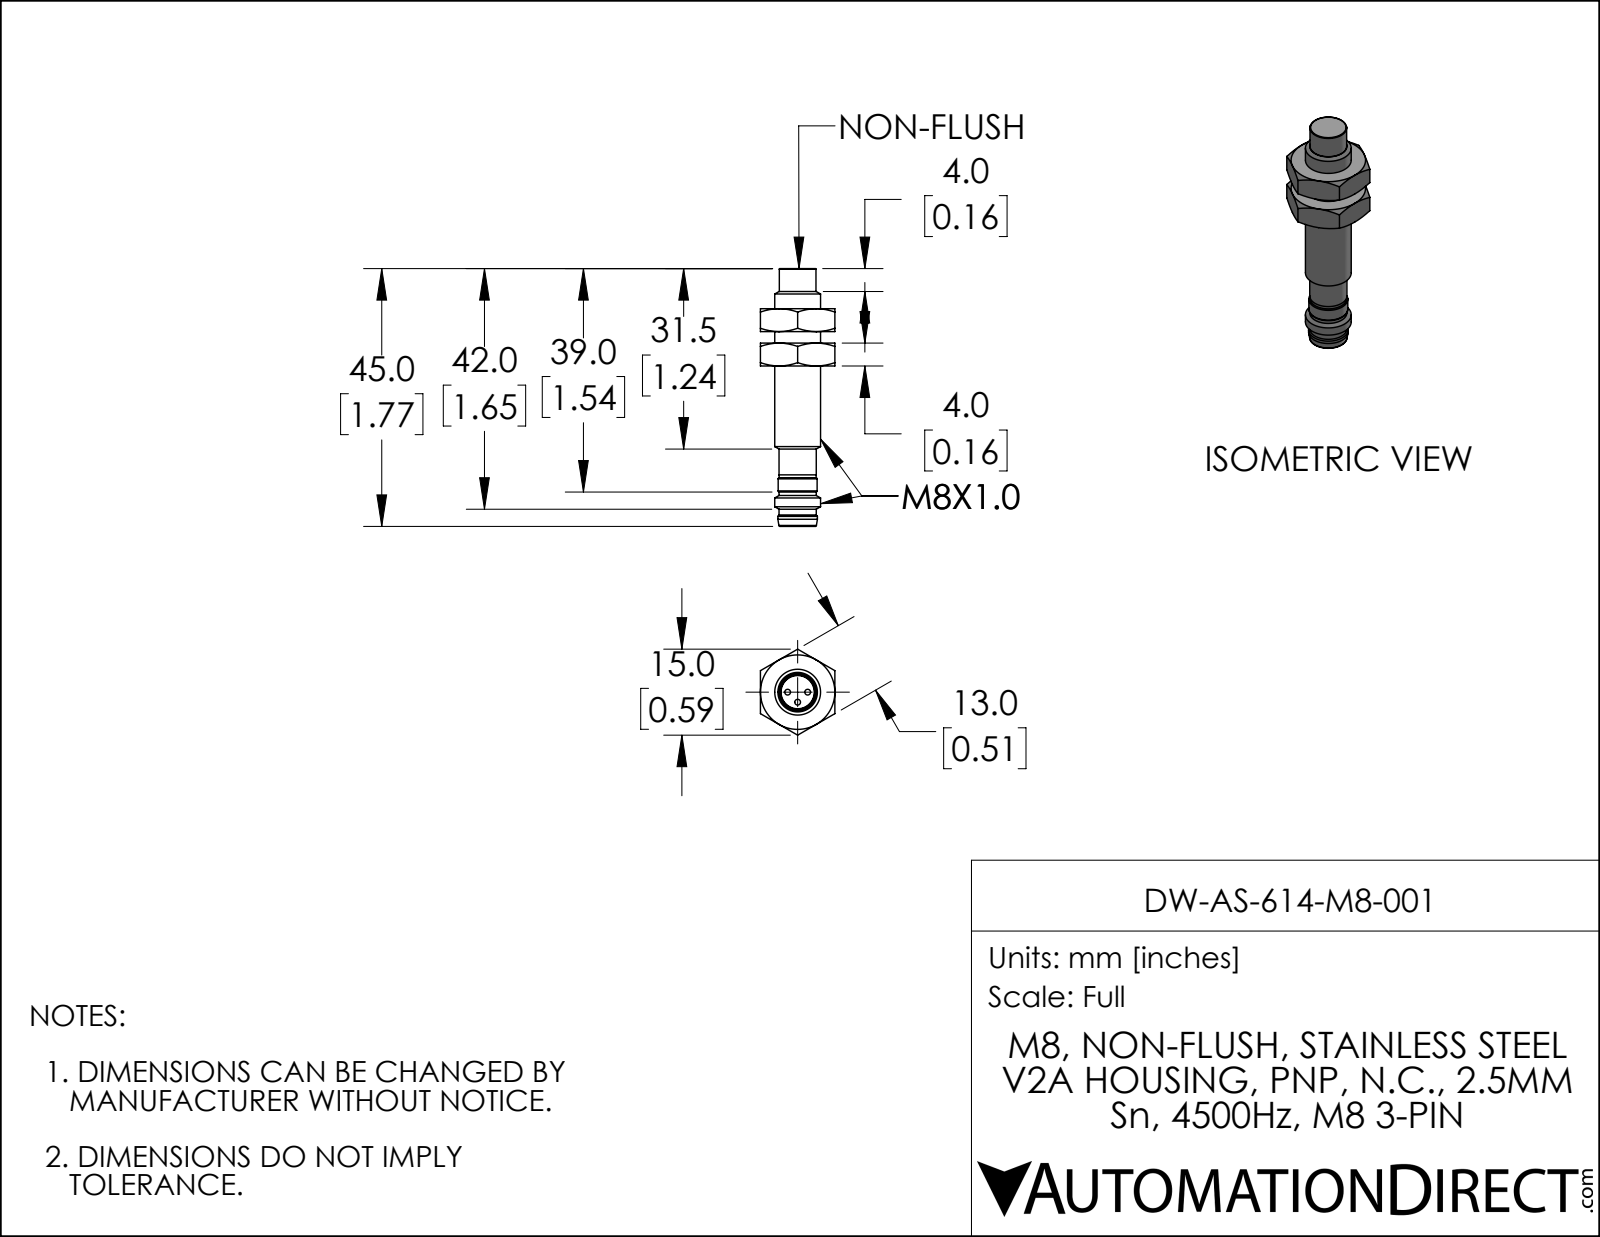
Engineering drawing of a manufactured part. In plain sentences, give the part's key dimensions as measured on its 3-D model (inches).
The part is named "DW-AS-614-M8-001". Its 3-D file was written by "SolidWorks 2019 (AUTOMOTIVE_DESIGN)". It is 1 solid with 76 faces: 24 planar, 15 cylindrical and 37 other. Overall it measures 1.772 by 0.591 by 0.512 inches. Its volume is 0.161 cubic inches and its surface area 2.817 square inches. Round holes: 1 of diameter 0.228. Round bosses or shafts: 3 of diameter 0.039, 1 of diameter 0.315, 1 of diameter 0.272, 1 of diameter 0.268, 1 of diameter 0.256, 1 of diameter 0.254, 1 of diameter 0.252. The main face-to-face distances are 0.512, 0.157, 0.236, 0.079, 0.394, 0.276, 0.433, 0.669, 1.142, 0.906.
